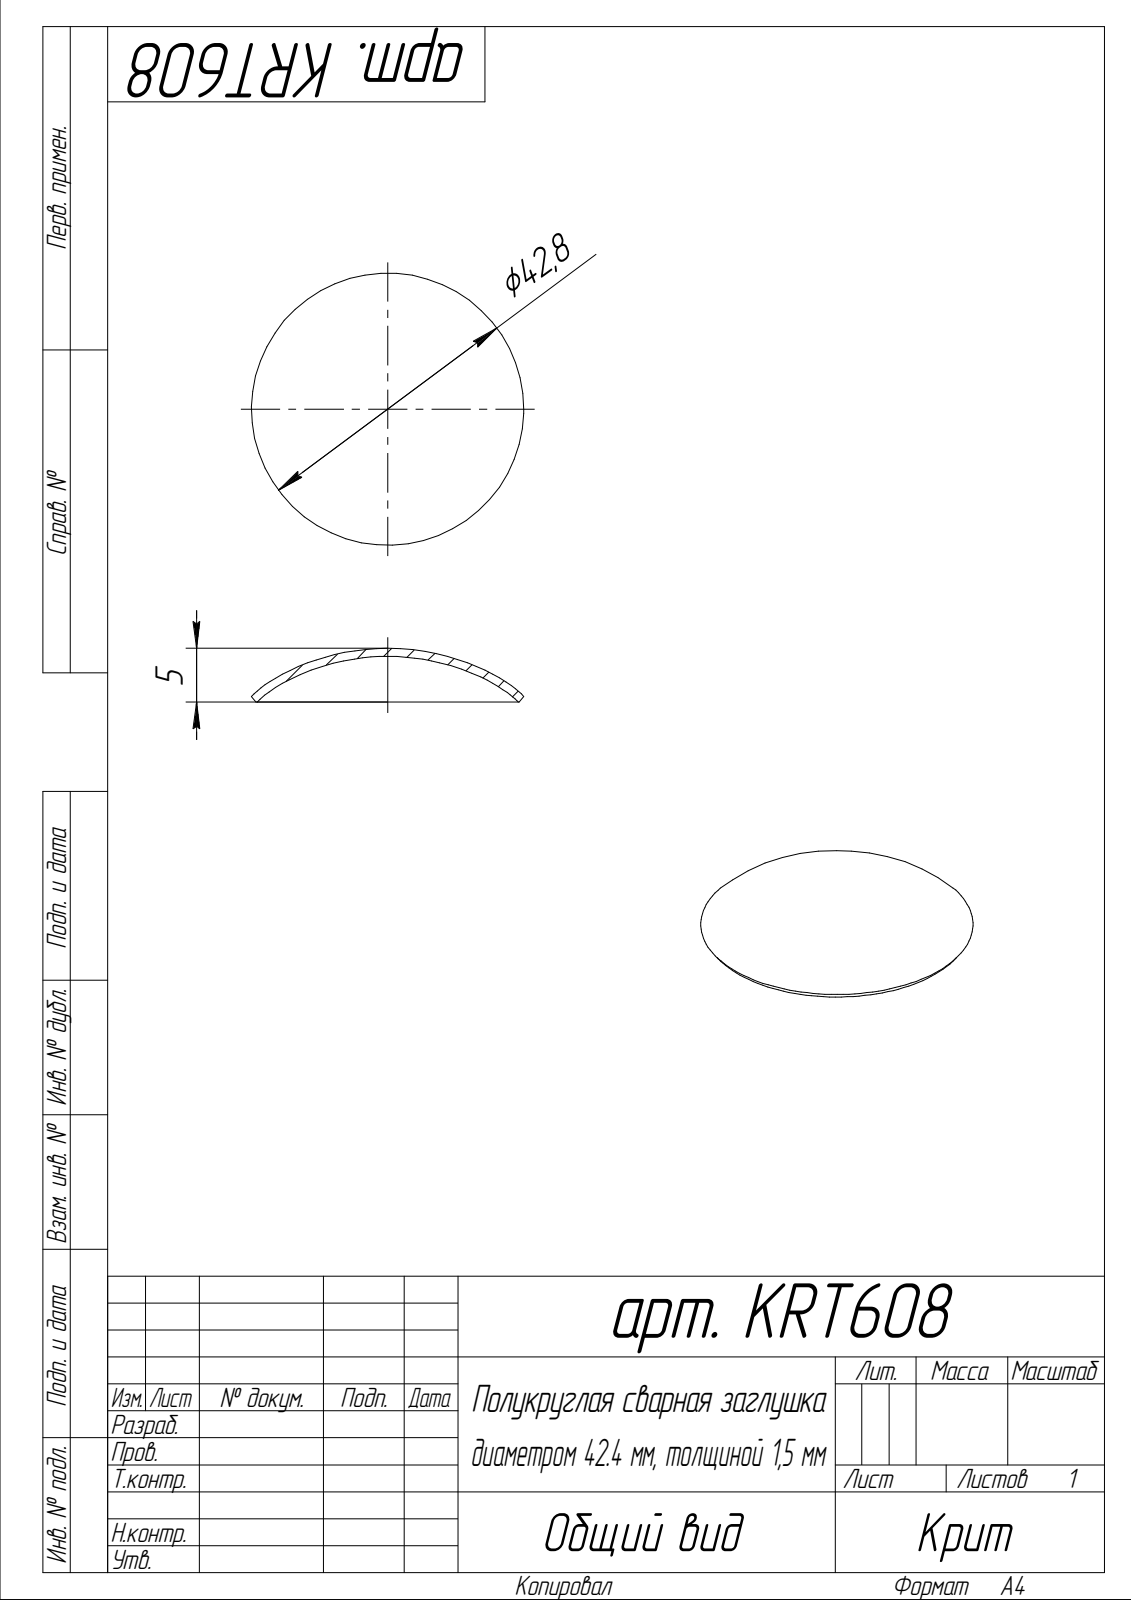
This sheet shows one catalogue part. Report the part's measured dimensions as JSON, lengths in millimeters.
{"part_name": "арт. KRT608", "step_written_by": "SolidWorks 2014 (AUTOMOTIVE_DESIGN)", "units": "millimeters", "bodies": {"solids": 1, "faces": 8, "planar": 0, "cylindrical": 0, "other": 8}, "overall_size": [42.8, 42.8, 6.14], "volume_mm3": 2178, "surface_area_mm2": 3111}
